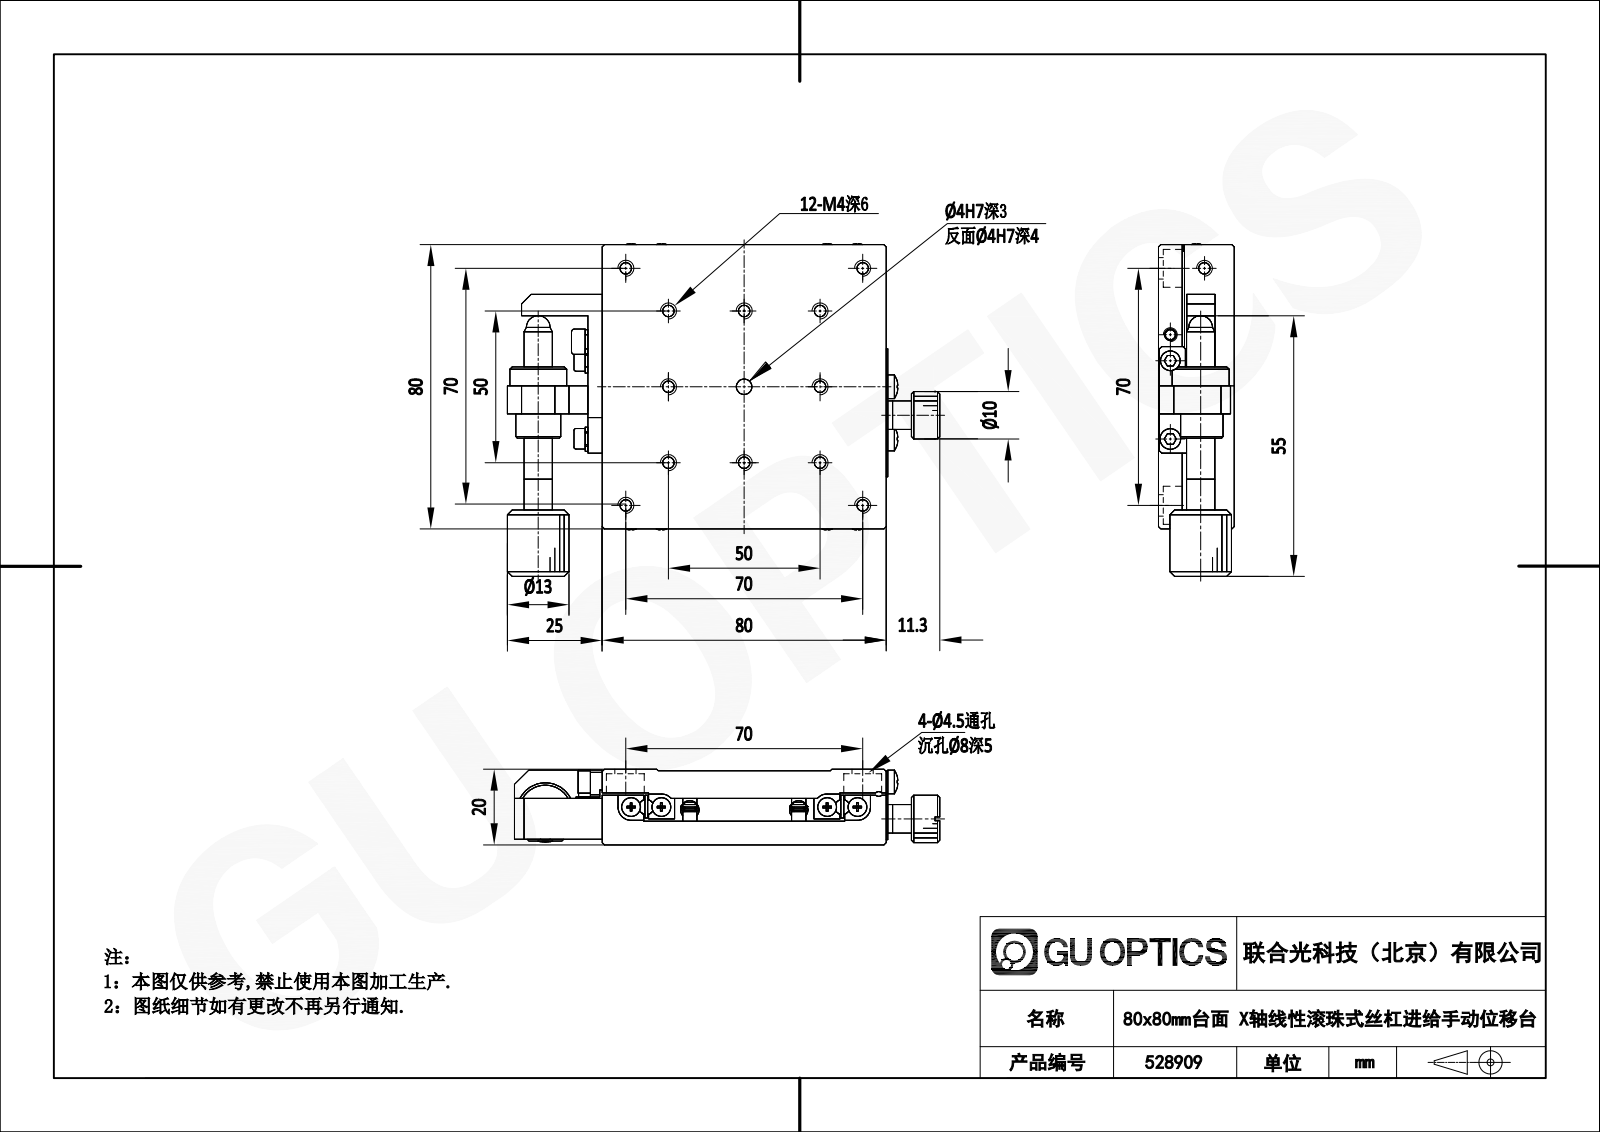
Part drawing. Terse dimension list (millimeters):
name: 528909
written by: SolidWorks 2020 (CONFIG_CONTROL_DESIGN)
unit: mm
bodies: 0 solids, 782 faces (387 planar, 232 cylindrical, 163 other)
size: 116.5 × 90 × 20
holes: 4× ⌀6, 2× ⌀3.5, 1× ⌀2.5, 1× ⌀7
bosses: 17× ⌀2.5, 12× ⌀3.3, 4× ⌀8, 4× ⌀4.5, 2× ⌀2.05, 1× ⌀12, 1× ⌀9.5, 1× ⌀6
rounds: 4× R2, 4× R3, 2× R1.75, 1× R1, 1× R5, 1× R6.5
face distances: 7, 12.65, 19.65, 6.5, 13, 12.8, 5.8, 6.85, 80, 20
hole spacings: 7.5, 6.5, 9, 10.89, 12.03, 15, 15.35, 16.5
